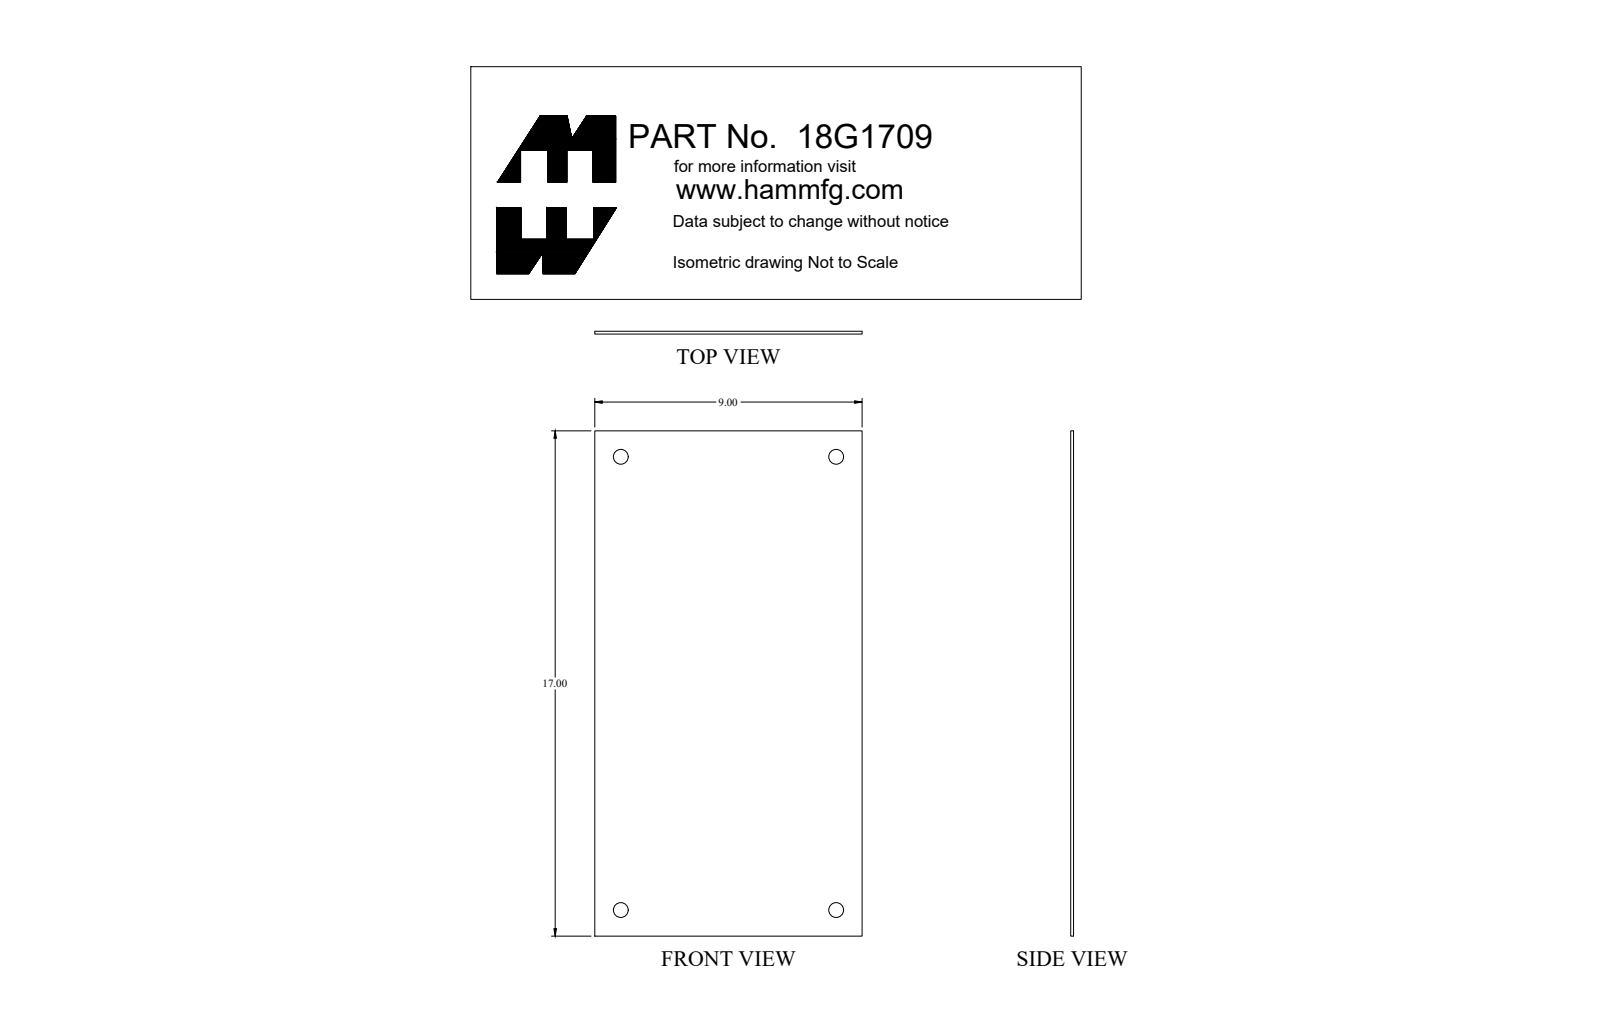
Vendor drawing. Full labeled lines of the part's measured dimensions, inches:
Part name (STEP PRODUCT): 18G1709
STEP written by: SolidWorks 2018 (AUTOMOTIVE_DESIGN)
Units: inches
Bodies: 1 solid, 10 faces (6 planar, 4 cylindrical, 0 other)
Overall size (bounding box): 17 × 9 × 0.095
Volume: 14.46 in³ · Surface area: 310 in²
Round holes (diameter × count): ⌀0.5 ×4
Main face-to-face distances: 0.095, 9, 17
Hole centre spacings: 7.25, 15.25, 16.885
